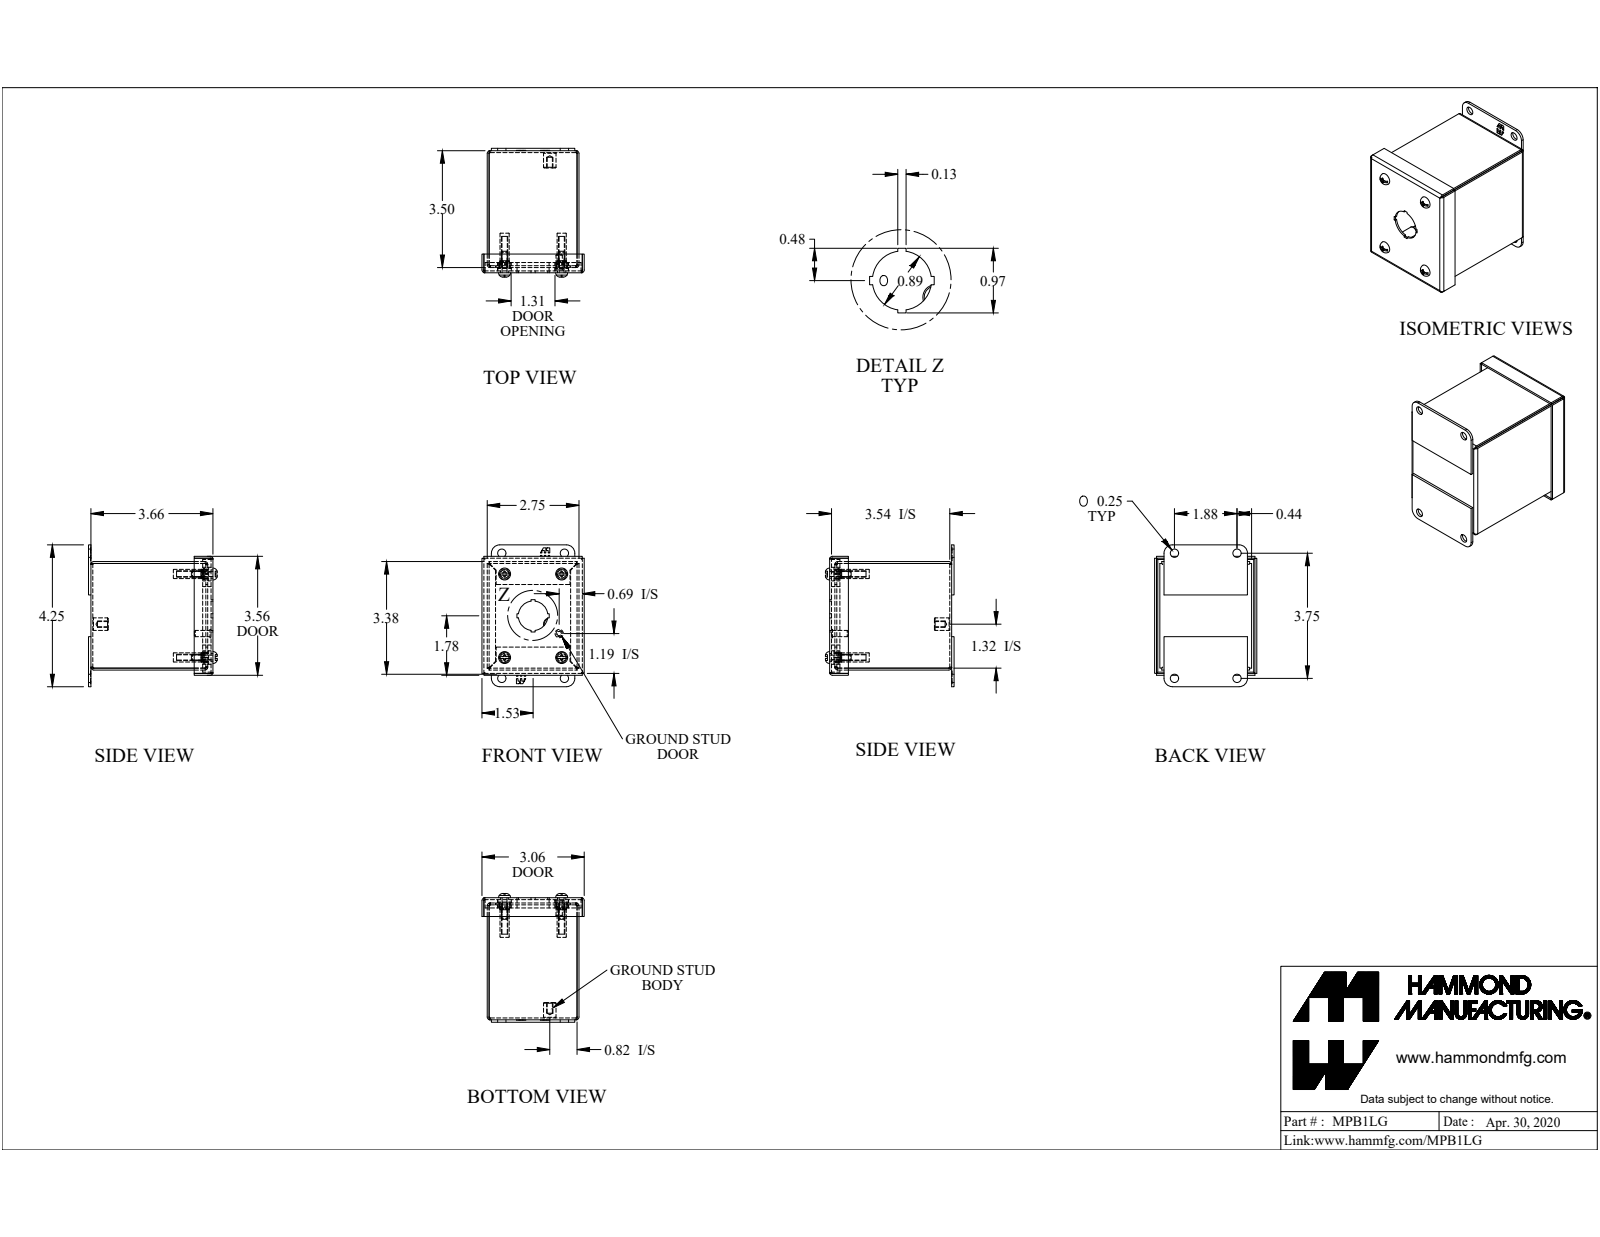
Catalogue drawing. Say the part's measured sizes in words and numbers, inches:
The part is named "MPB1LG". Its 3-D file was written by "SolidWorks 2019 (AUTOMOTIVE_DESIGN)". It is 19 solids with 443 faces: 307 planar, 100 cylindrical and 36 other. Overall it measures 4.25 by 3.856 by 3.063 inches. Its volume is 5.871 cubic inches and its surface area 183.1 square inches. Round holes: 8 of diameter 0.25, 4 of diameter 0.159, 4 of diameter 0.406, 1 of diameter 0.156, 1 of diameter 0.886. Round bosses or shafts: 4 of diameter 0.39, 4 of diameter 0.19, 4 of diameter 0.148, 2 of diameter 0.275, 2 of diameter 0.275, 1 of diameter 0.375, 1 of diameter 0.25, 1 of diameter 0.188. Partial cylindrical surfaces (rounded edges, fillets, slot ends): 12 of radius 0.029, 12 of radius 0.086, 4 of radius 0.16, 4 of radius 0.171, 4 of radius 0.25. The main face-to-face distances are 0.057, 0.057, 3.6, 2.693, 3.193, 2.75, 2.636, 3.657, 3.136, 3.25. The hole center spacings are 1.899, 1.711, 0.63, 2.5, 3.127, 3.603, 1.515, 1.709.
